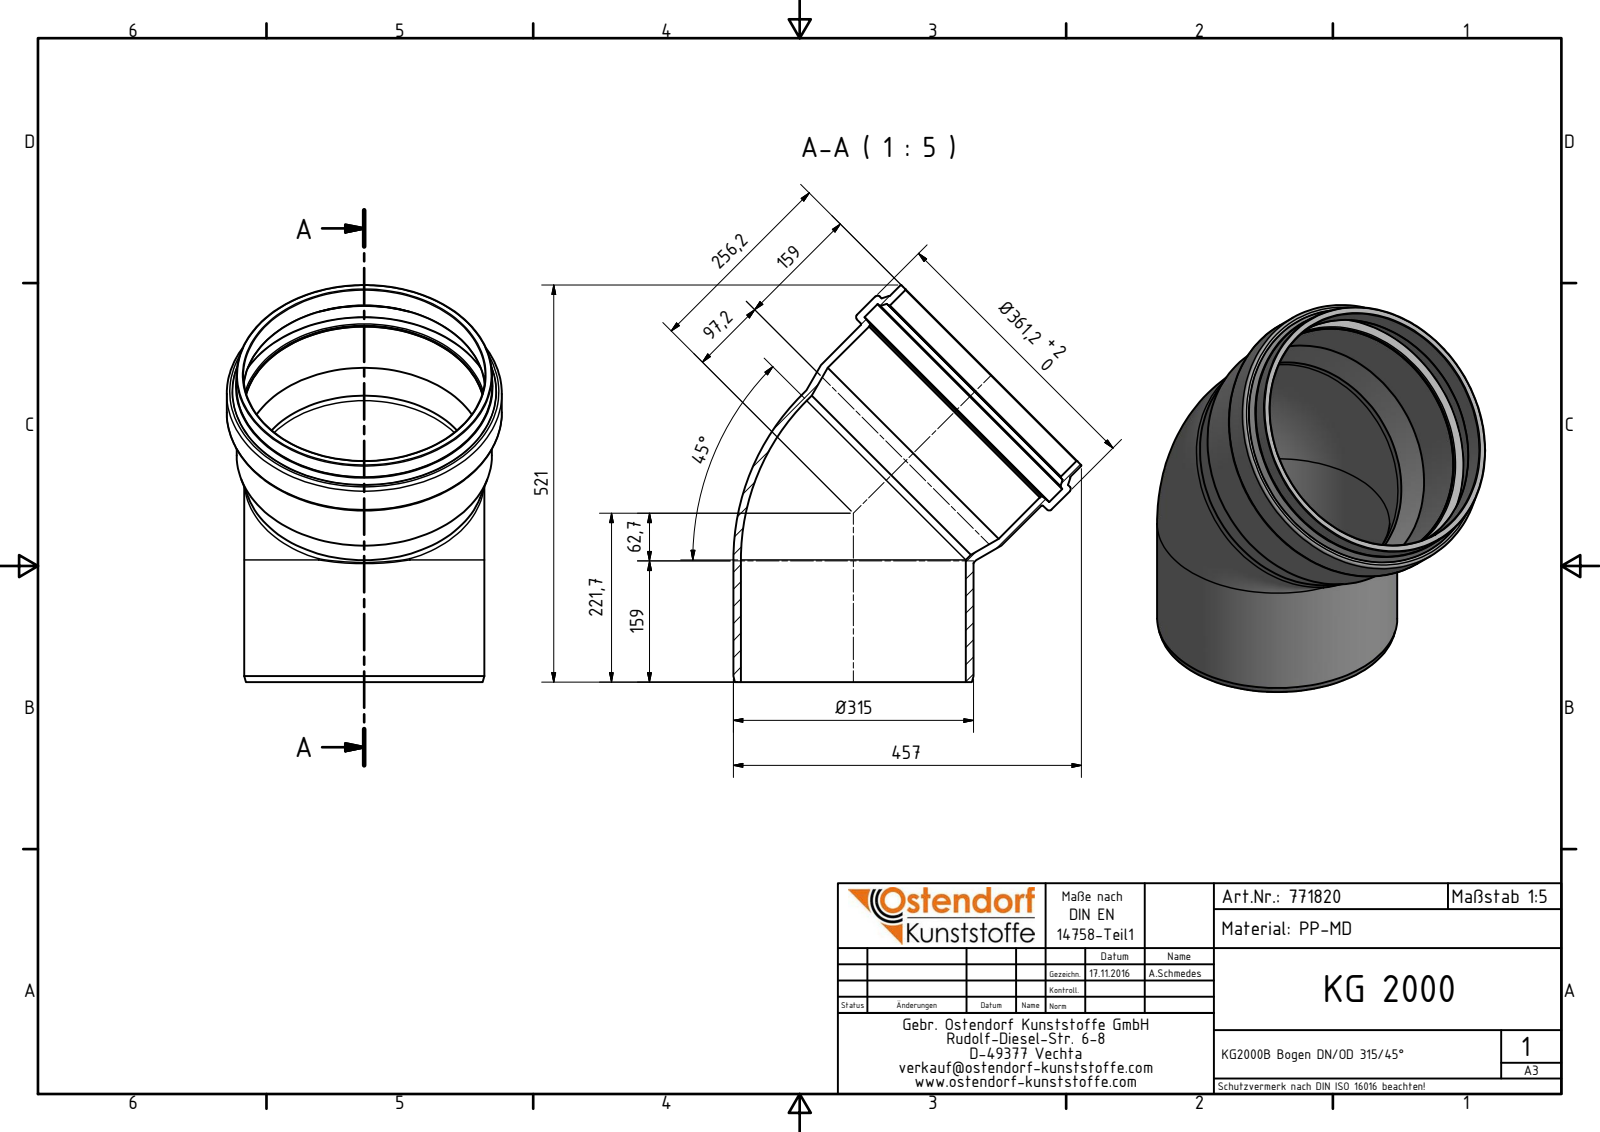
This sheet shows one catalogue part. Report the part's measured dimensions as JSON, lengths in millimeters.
{"part_name": "771820 KG2000B Bogen DN_OD 315_45°", "step_written_by": "Autodesk Inventor 2016 (AUTOMOTIVE_DESIGN)", "units": "millimeters", "bodies": {"solids": 1, "faces": 41, "planar": 5, "cylindrical": 11, "other": 25}, "overall_size": [521, 457, 361.2], "volume_mm3": 4410000, "surface_area_mm2": 990944, "round_holes": [[295.3, 2], [317.5, 2], [317.1, 1], [343.2, 1]], "round_bosses_or_shafts": [[315.3, 2], [361.2, 1], [335.5, 1], [335.1, 1]], "face_to_face_distances": [73.09, 42.39, 30.7, 4.55, 37.84, 68.54]}
